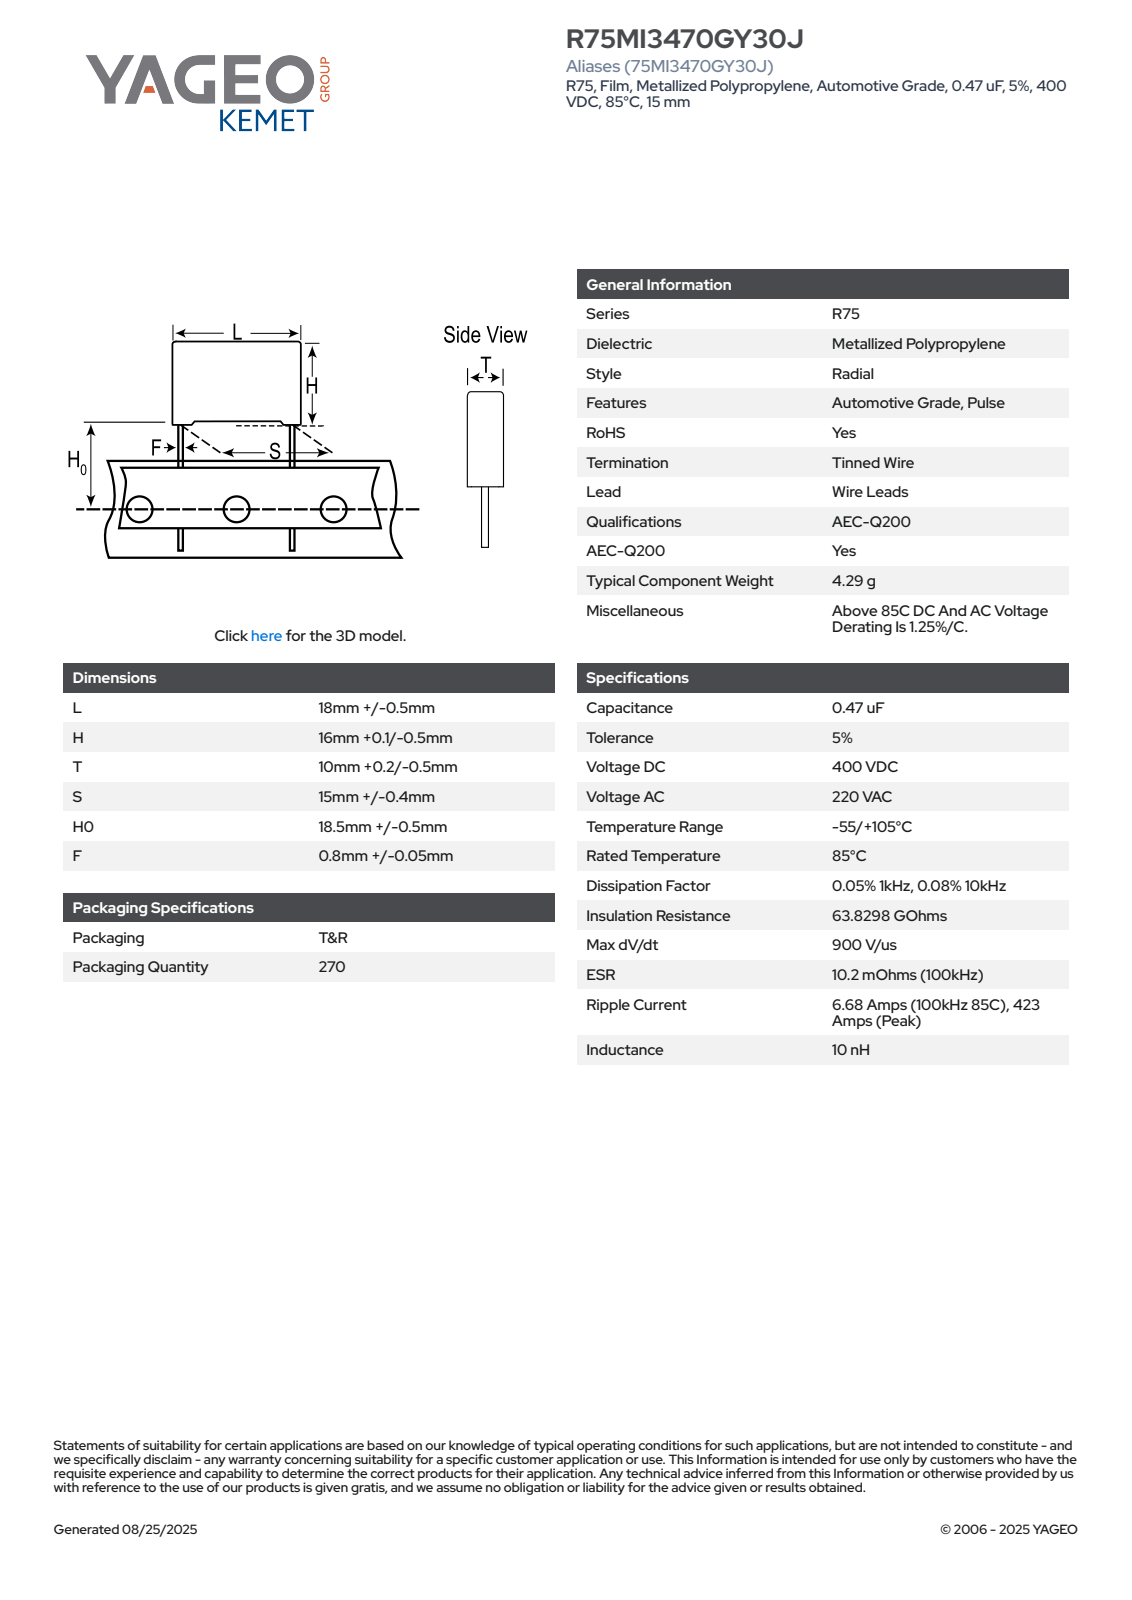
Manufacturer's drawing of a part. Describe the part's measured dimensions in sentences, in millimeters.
The part is named "CFR_RB2_18X16X10_L18.5H16.1T10.2S15H019F0.85". Its 3-D file was written by "SolidWorks 2020 (AUTOMOTIVE_DESIGN)". It is 4 solids with 85 faces: 77 planar, 8 cylindrical and 0 other. Overall it measures 35.1 by 18.5 by 10.21 millimeters. Its volume is 2 934 cubic millimeters and its surface area 1 435 square millimeters. Round bosses or shafts: 2 of diameter 0.85. Partial cylindrical surfaces (rounded edges, fillets, slot ends): 4 of radius 0.5. The main face-to-face distances are 10.2, 18.5, 15.35, 0.62, 0.75, 16.1, 0.56, 15.54, 17.88, 9.58.
